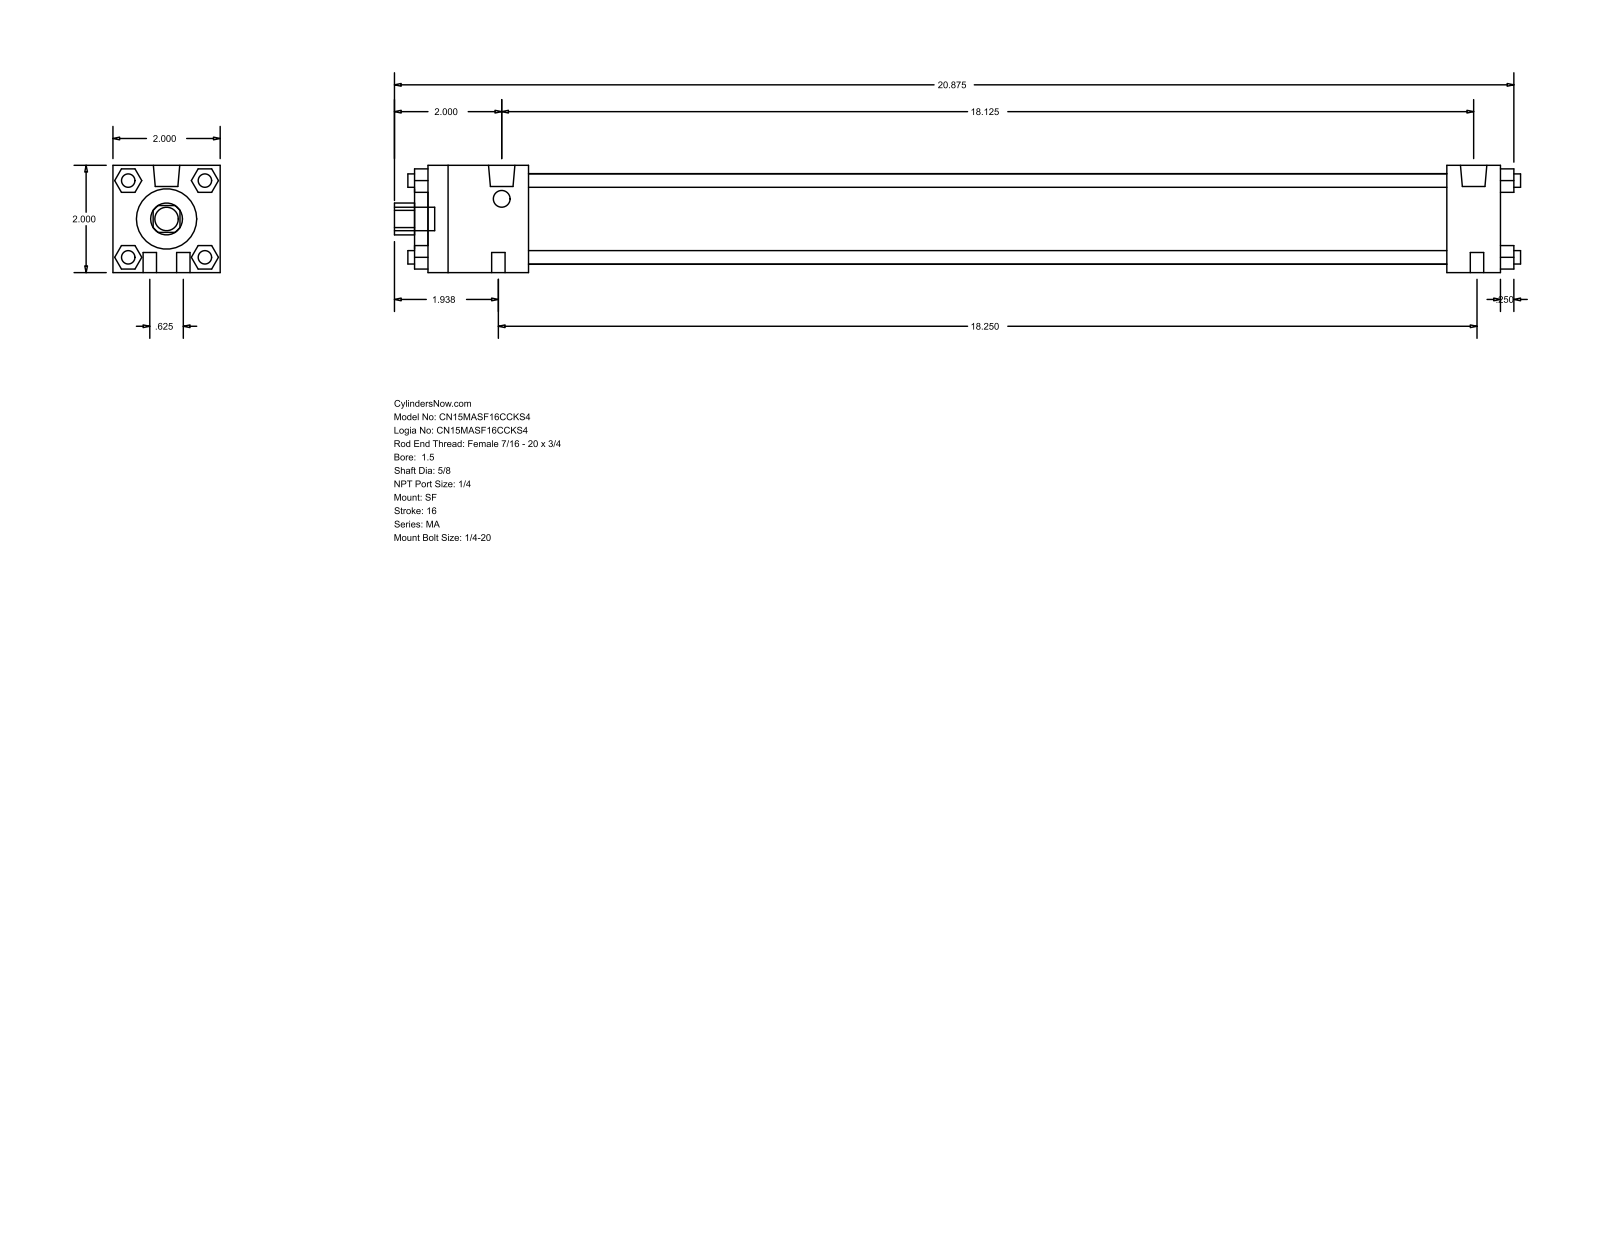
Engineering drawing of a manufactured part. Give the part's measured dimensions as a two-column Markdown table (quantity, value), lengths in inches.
| quantity | value |
| --- | --- |
| part name | MA_SF__0150_0.625 |
| STEP written by | GSSL Pune (CONFIG_CONTROL_DESIGN) |
| units | inches |
| bodies | 0 solids, 124 faces (94 planar, 30 cylindrical, 0 other) |
| overall size | 21 × 2 × 2 |
| round holes (diameter × count) | 0.625 × 1, 1.125 × 1, 1.69 × 1 |
| round bosses / shafts (diameter × count) | 0.25 × 8, 0.492 × 2, 0.313 × 2, 0.437 × 1 |
| partial cylindrical surfaces (radius × count) | 0.297 × 1 |
| main face-to-face distances | 2, 20, 0.25, 20.25, 1.875, 19, 17.125, 18.125, 1, 2.125 |
